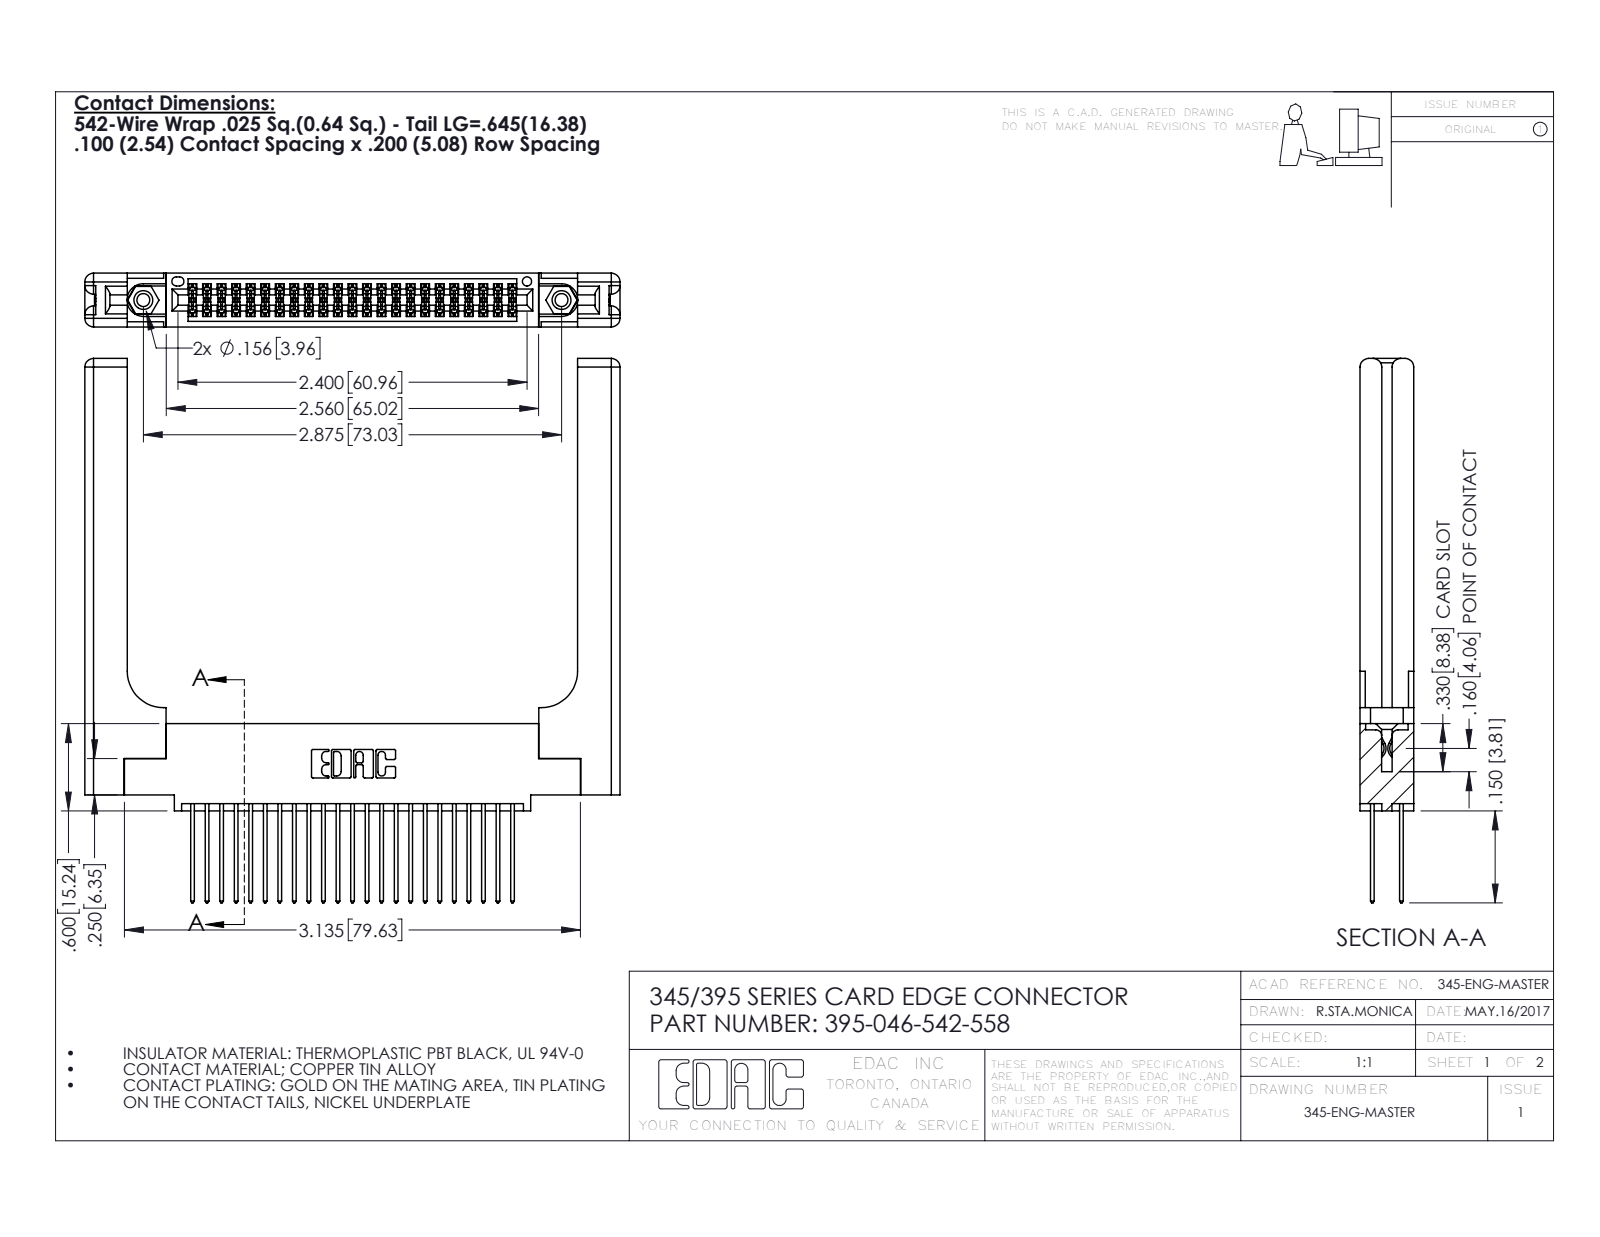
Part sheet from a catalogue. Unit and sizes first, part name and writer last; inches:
Units: inches
Overall size (bounding box): 3.742 × 3.679 × 0.37
Round holes (diameter × count): ⌀0.089 ×2, ⌀0.125 ×2, ⌀0.156 ×2, ⌀0.064 ×1
Round bosses / shafts (diameter × count): ⌀0.155 ×2
Partial cylindrical surfaces — rounded edges, fillets, slot ends (radius × count): R0.006 ×69, R0.01 ×46, R0.01 ×22, R0.06 ×16, R0.007 ×6, R0.031 ×6, R0.026 ×3, R0.014 ×2
Main face-to-face distances: 0.072, 0.37, 0.298, 0.098, 0.272, 0.025, 0.2, 0.225, 0.15, 0.148
Hole centre spacings: 0.27, 2.641, 2.875
Volume: 1.069 in³ · Surface area: 29.69 in²
Bodies: 51 solids, 2686 faces (1750 planar, 876 cylindrical, 60 other)
Part name (STEP PRODUCT): 345 Part_0.110 Offset - 0.156 Dia-TH; 345-292-001_345-293-142; 395-046-542-558; 345-250-001_345-250-001-102 (+1 more)
STEP written by: SolidWorks 2016 (CONFIG_CONTROL_DESIGN)
